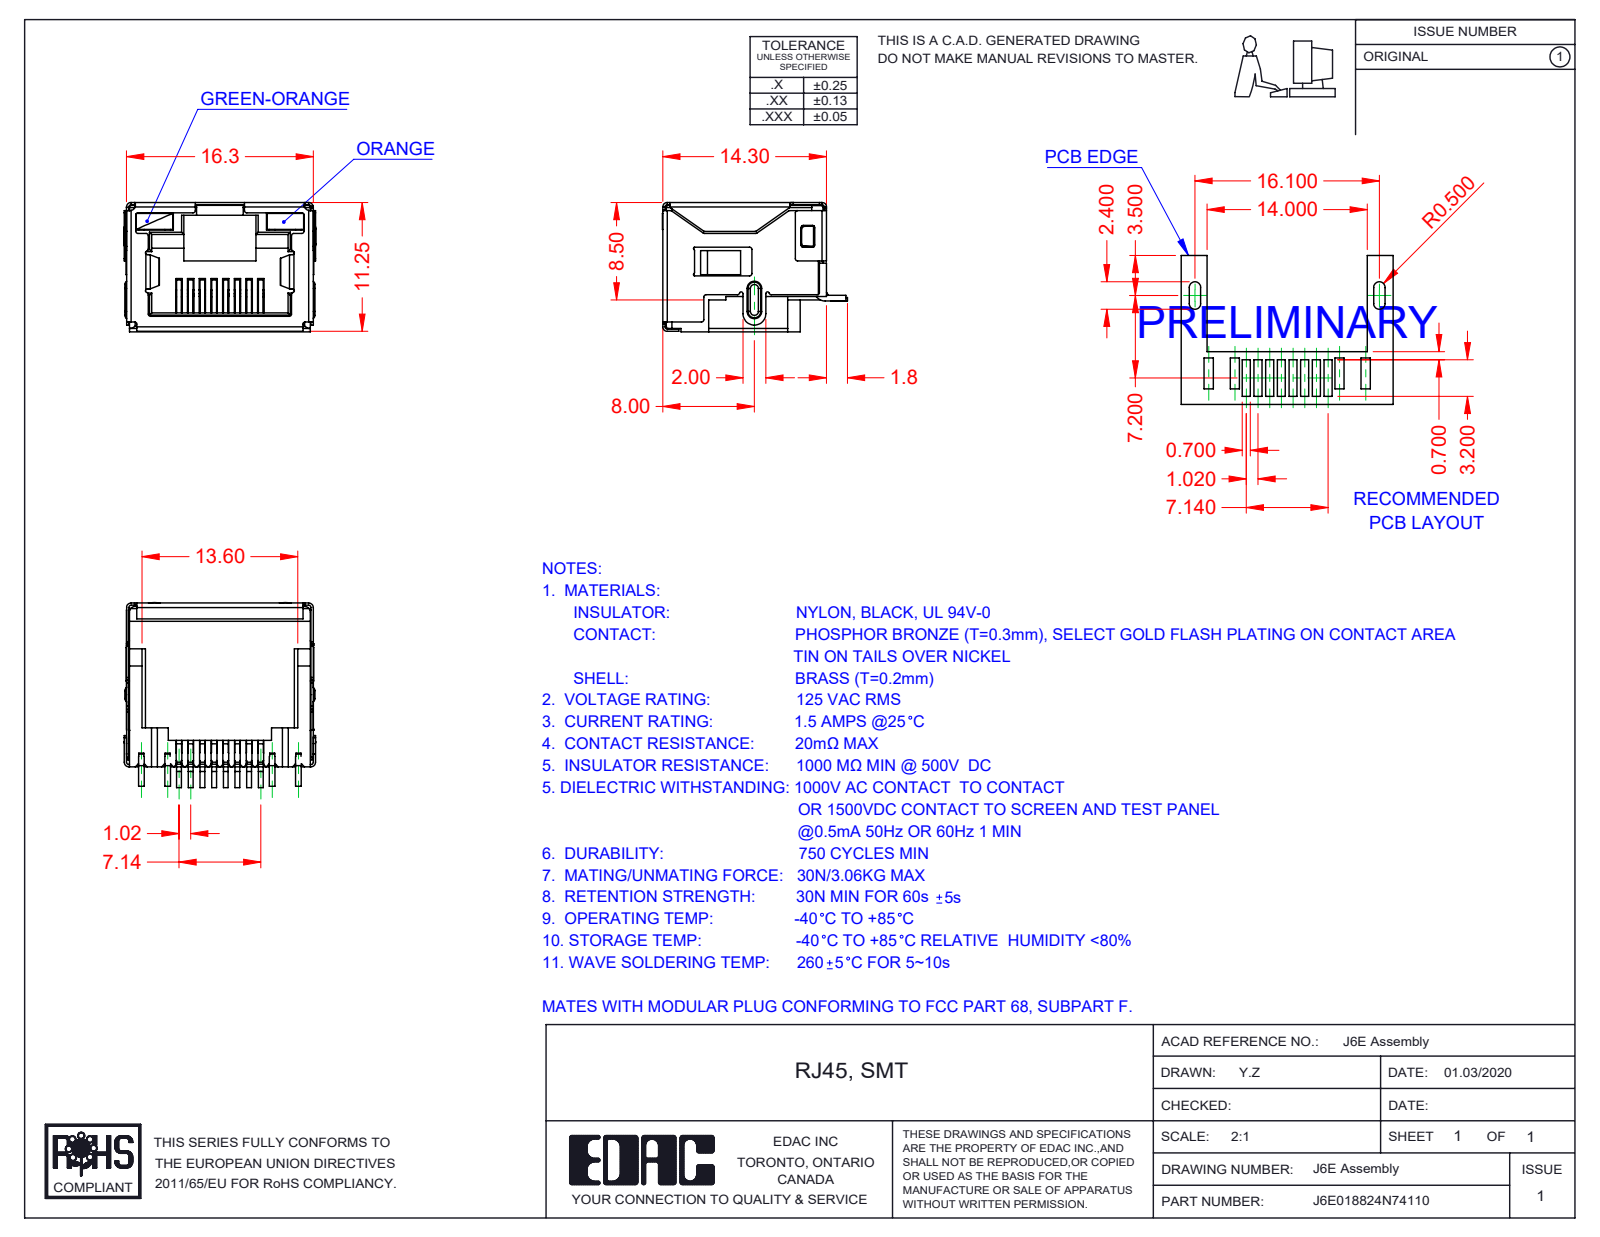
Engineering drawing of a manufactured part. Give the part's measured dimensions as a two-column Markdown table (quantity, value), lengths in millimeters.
| quantity | value |
| --- | --- |
| part name | 6E Shield_LED; J6E018824N74110; 6E LED RH_4-Orange; 6E LED LH_7-Green-Orange (+2 more) |
| STEP written by | SolidWorks 2016 (CONFIG_CONTROL_DESIGN) |
| units | millimeters |
| bodies | 12 solids, 1498 faces (1099 planar, 349 cylindrical, 50 other) |
| overall size | 16.75 × 16.15 × 11.3 |
| volume | 1 109 mm³ |
| surface area | 4 045 mm² |
| partial cylindrical surfaces (radius × count) | 0.2 × 82, 0.25 × 17, 0.4 × 13, 0.5 × 13, 0.1 × 10, 0.15 × 7, 0.3 × 4, 1 × 3 |
| main face-to-face distances | 11.05, 16.05, 16.1, 15.85, 11.1, 11.3, 2.4, 0.7, 9.85, 0.49 |
